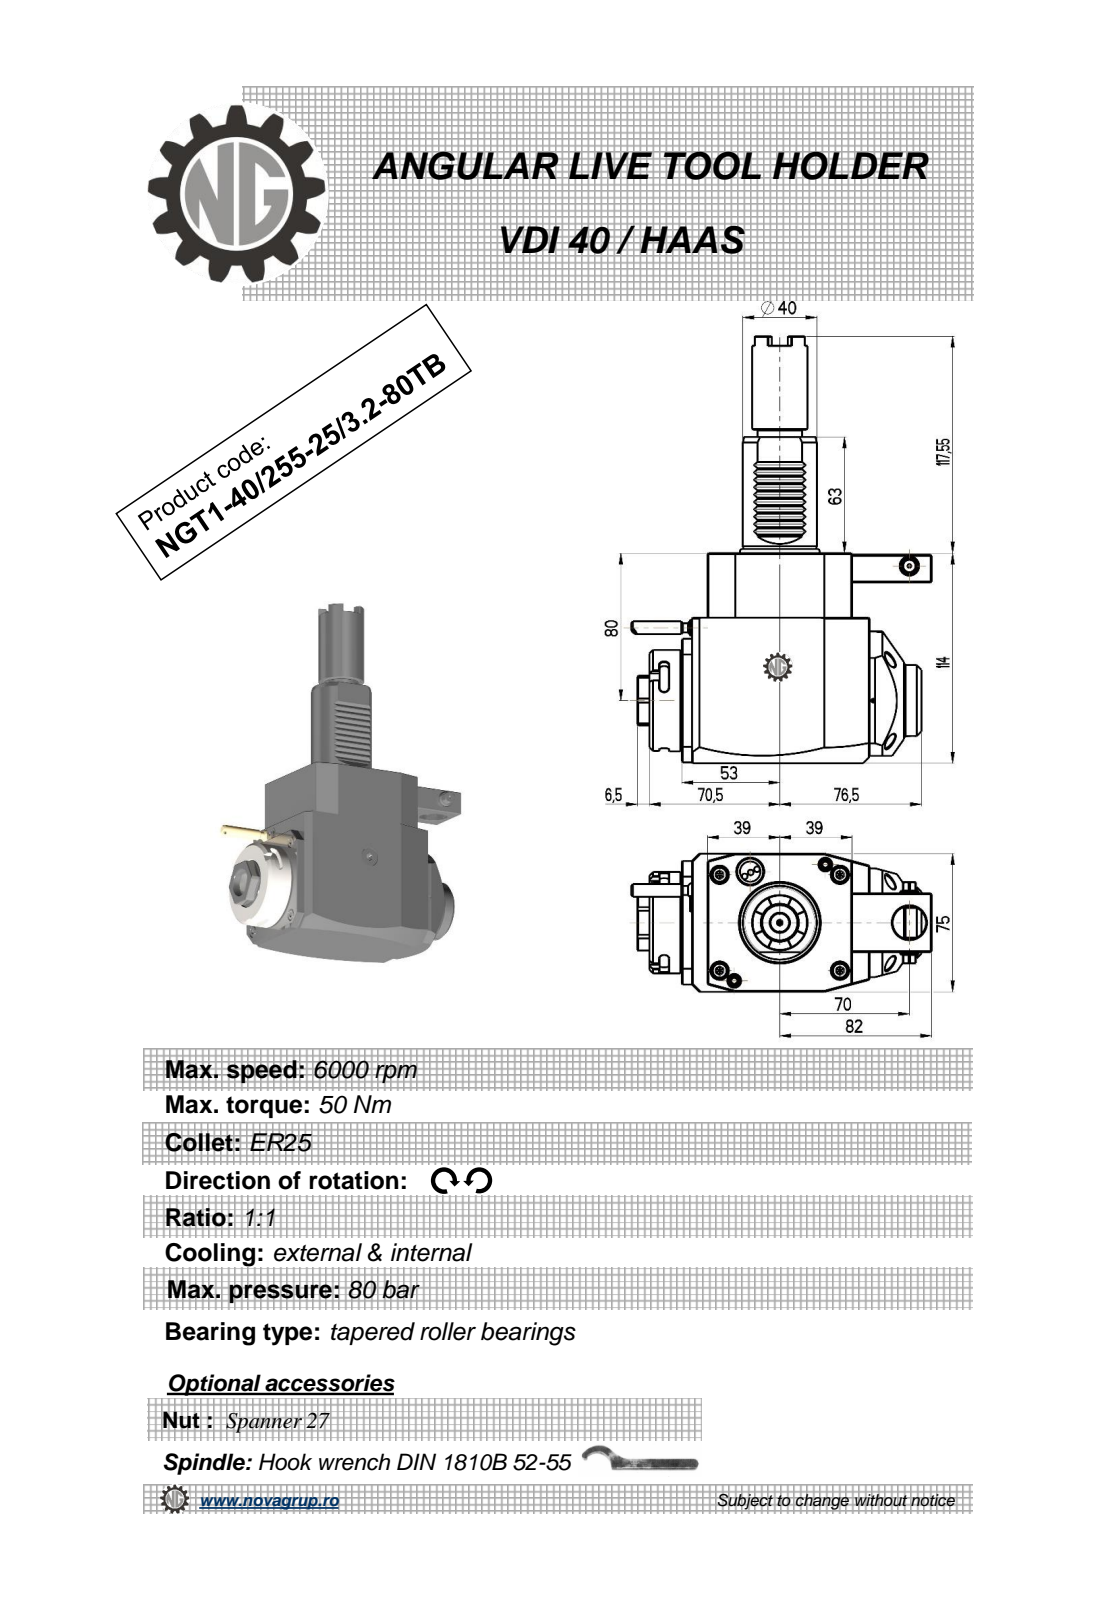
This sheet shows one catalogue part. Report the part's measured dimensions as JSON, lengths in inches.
{"part_name": "NGT1_40_255_25_3_2_80TB", "step_written_by": "PRO/ENGINEER BY PARAMETRIC TECHNOLOGY CORPORATION, 2010280 (CONFIG_CONTROL_DESIGN)", "units": "inches", "bodies": {"solids": 1, "faces": 397, "planar": 213, "cylindrical": 94, "other": 90}, "overall_size": [9.116, 6.391, 2.953], "volume_in3": 61.57, "surface_area_in2": 122, "round_holes": [[0.709, 2], [0.079, 1], [0.098, 1], [0.118, 1], [0.374, 1], [0.787, 1]], "round_bosses_or_shafts": [[0.353, 2], [2.165, 1], [1.89, 1], [1.575, 1], [1.516, 1], [1.181, 1], [0.945, 1], [0.394, 1]], "partial_cylinders_radius": [[0.012, 10], [0.098, 6], [7.087, 2], [0.02, 1], [0.152, 1], [0.167, 1], [0.591, 1], [0.965, 1]], "face_to_face_distances": [2.953, 4.488, 0.551, 0.689, 4.311, 3.11, 3.622, 3.071, 1.24, 3.858], "hole_center_spacings": [1.47, 1.701, 2.756, 2.854]}
